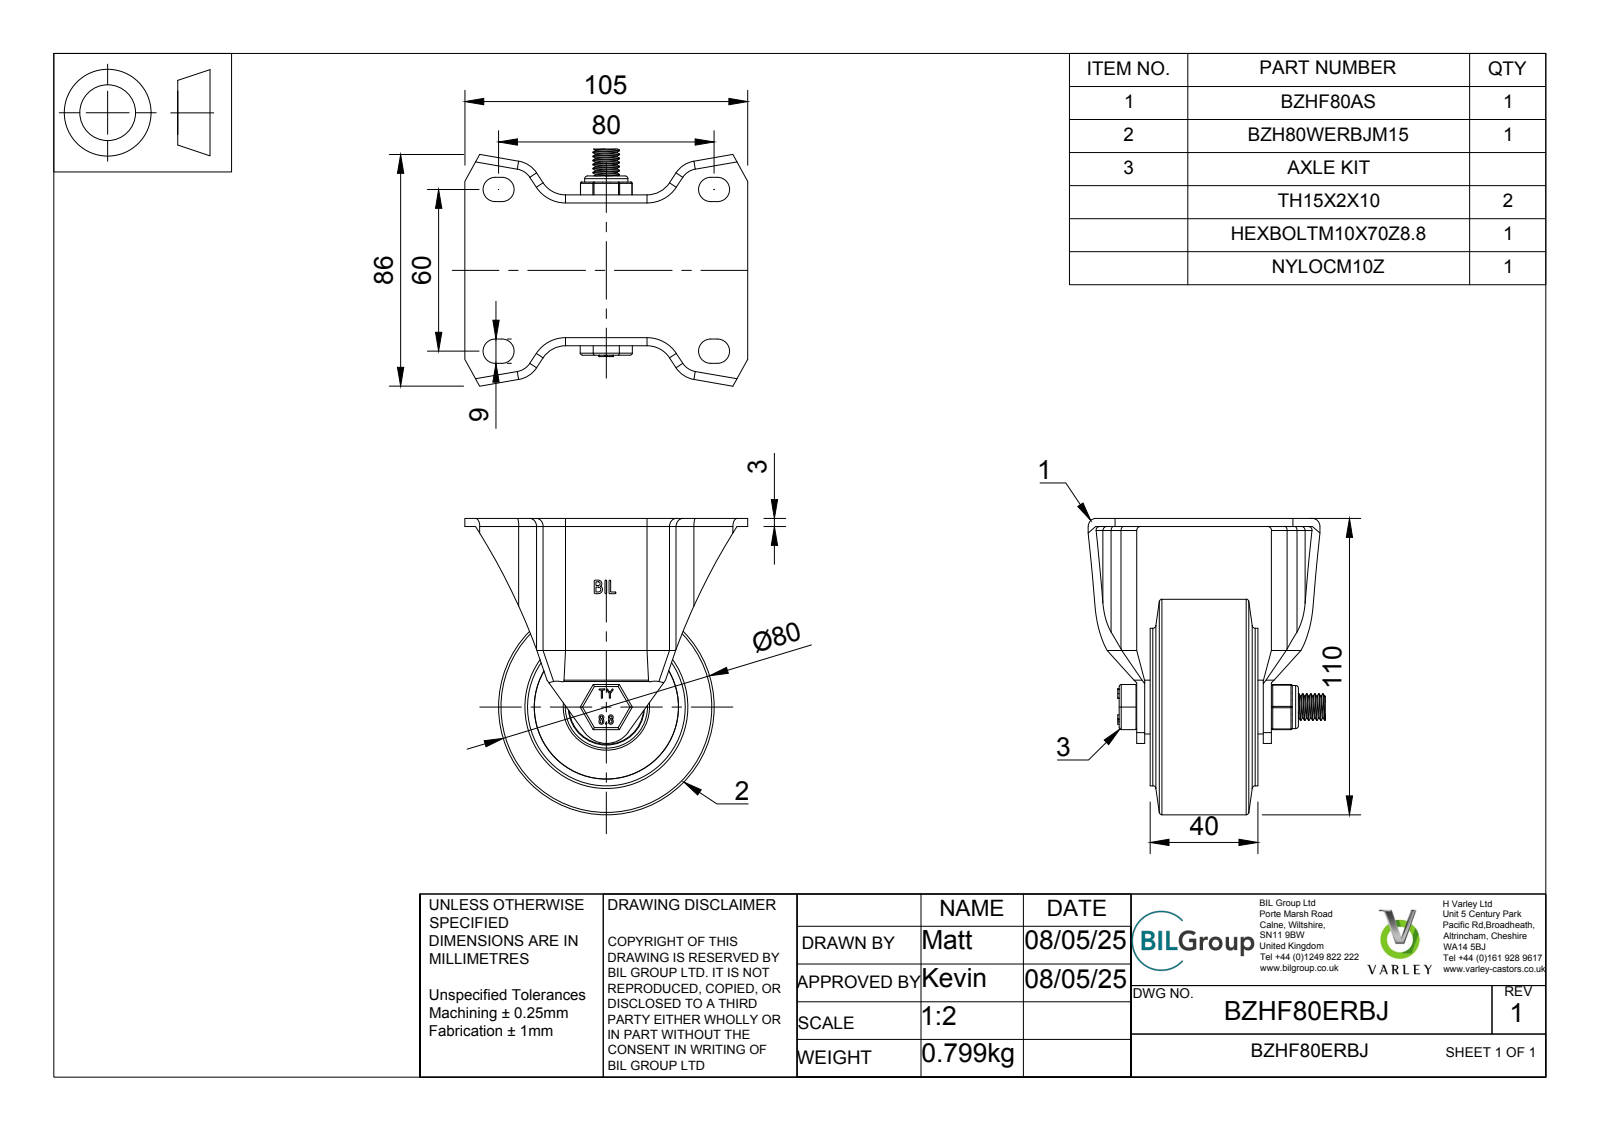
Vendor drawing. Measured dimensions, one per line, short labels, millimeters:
name: BZHF80ERBJ v4; BZHF80AS - 44 v1; BZHF80AS v1 (1); BZHF80AS (1) (+8 more)
written by: Autodesk Translation Framework v14.4.0.0 (AUTOMOTIVE_DESIGN)
unit: mm
bodies: 37 solids, 1137 faces (396 planar, 210 cylindrical, 531 other)
size: 110 × 105 × 88
volume: 231 520 mm³; area: 94 933 mm²
holes: 1× ⌀10, 1× ⌀10.2, 1× ⌀10.5, 1× ⌀12, 1× ⌀15, 1× ⌀20.5, 1× ⌀26.8, 1× ⌀28, 1× ⌀28.2, 1× ⌀32, 1× ⌀53.5
bosses: 1× ⌀80, 1× ⌀58.5, 1× ⌀21.5, 1× ⌀20, 1× ⌀19, 1× ⌀16, 1× ⌀14.75, 1× ⌀9.85
rounds: 18× R0.5, 10× R1.5, 10× R3, 9× R10, 8× R4.5, 6× R0.75, 4× R7, 4× R13
face distances: 3, 5, 45, 50, 8, 48, 53, 40, 31, 6
